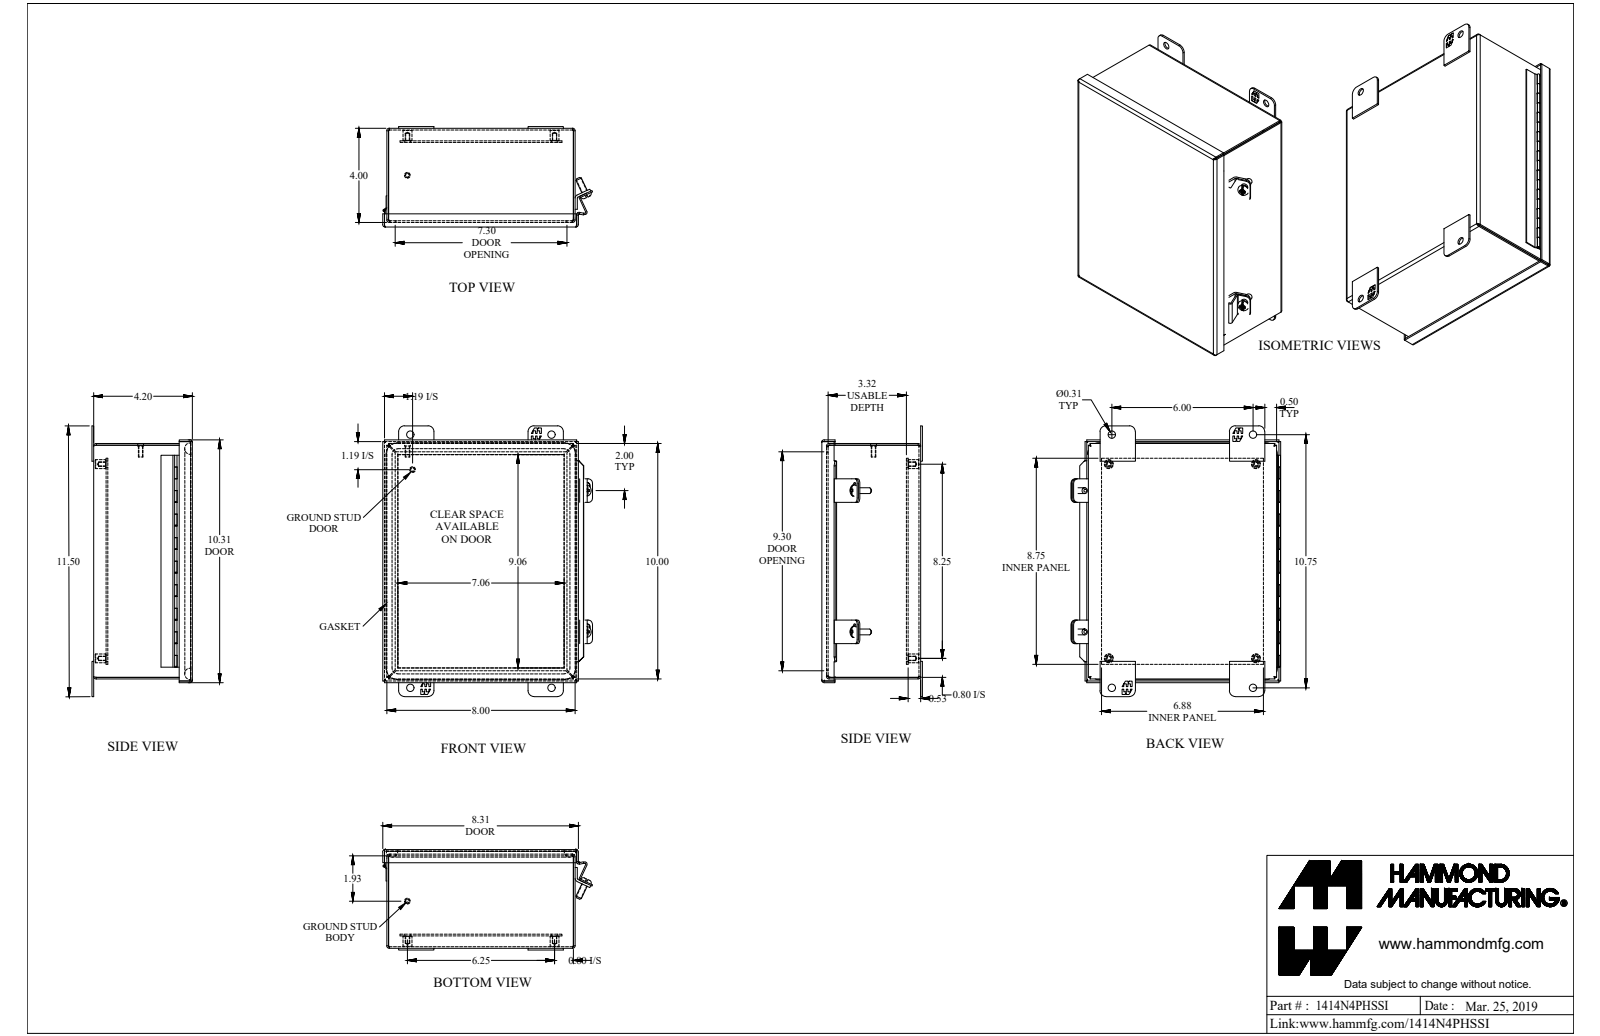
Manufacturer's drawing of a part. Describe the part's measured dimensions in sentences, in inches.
The part is named "1414N4PHSSI". Its 3-D file was written by "SolidWorks 2018 (AUTOMOTIVE_DESIGN)". It is 21 solids with 696 faces: 448 planar, 184 cylindrical and 64 other. Overall it measures 11.5 by 8.903 by 4.269 inches. Its volume is 33.2 cubic inches and its surface area 934.7 square inches. Round holes: 4 of diameter 0.156, 4 of diameter 0.265, 4 of diameter 0.313, 2 of diameter 0.213, 1 of diameter 0.05. Round bosses or shafts: 4 of diameter 0.375, 4 of diameter 0.25, 2 of diameter 0.48, 2 of diameter 0.19, 1 of diameter 0.1, 1 of diameter 0.045. Partial cylindrical surfaces (rounded edges, fillets, slot ends): 24 of radius 0.25, 9 of radius 0.036, 9 of radius 0.108, 8 of radius 0.188, 4 of radius 0.007, 4 of radius 0.046, 4 of radius 0.079, 4 of radius 0.118. The main face-to-face distances are 0.072, 4.125, 3.593, 0.532, 4.197, 4.053, 7.928, 0.604, 3.665, 0.46. The hole center spacings are 1.257, 6.252, 9.501, 10.35, 11.304, 6, 6.25, 6.25.
